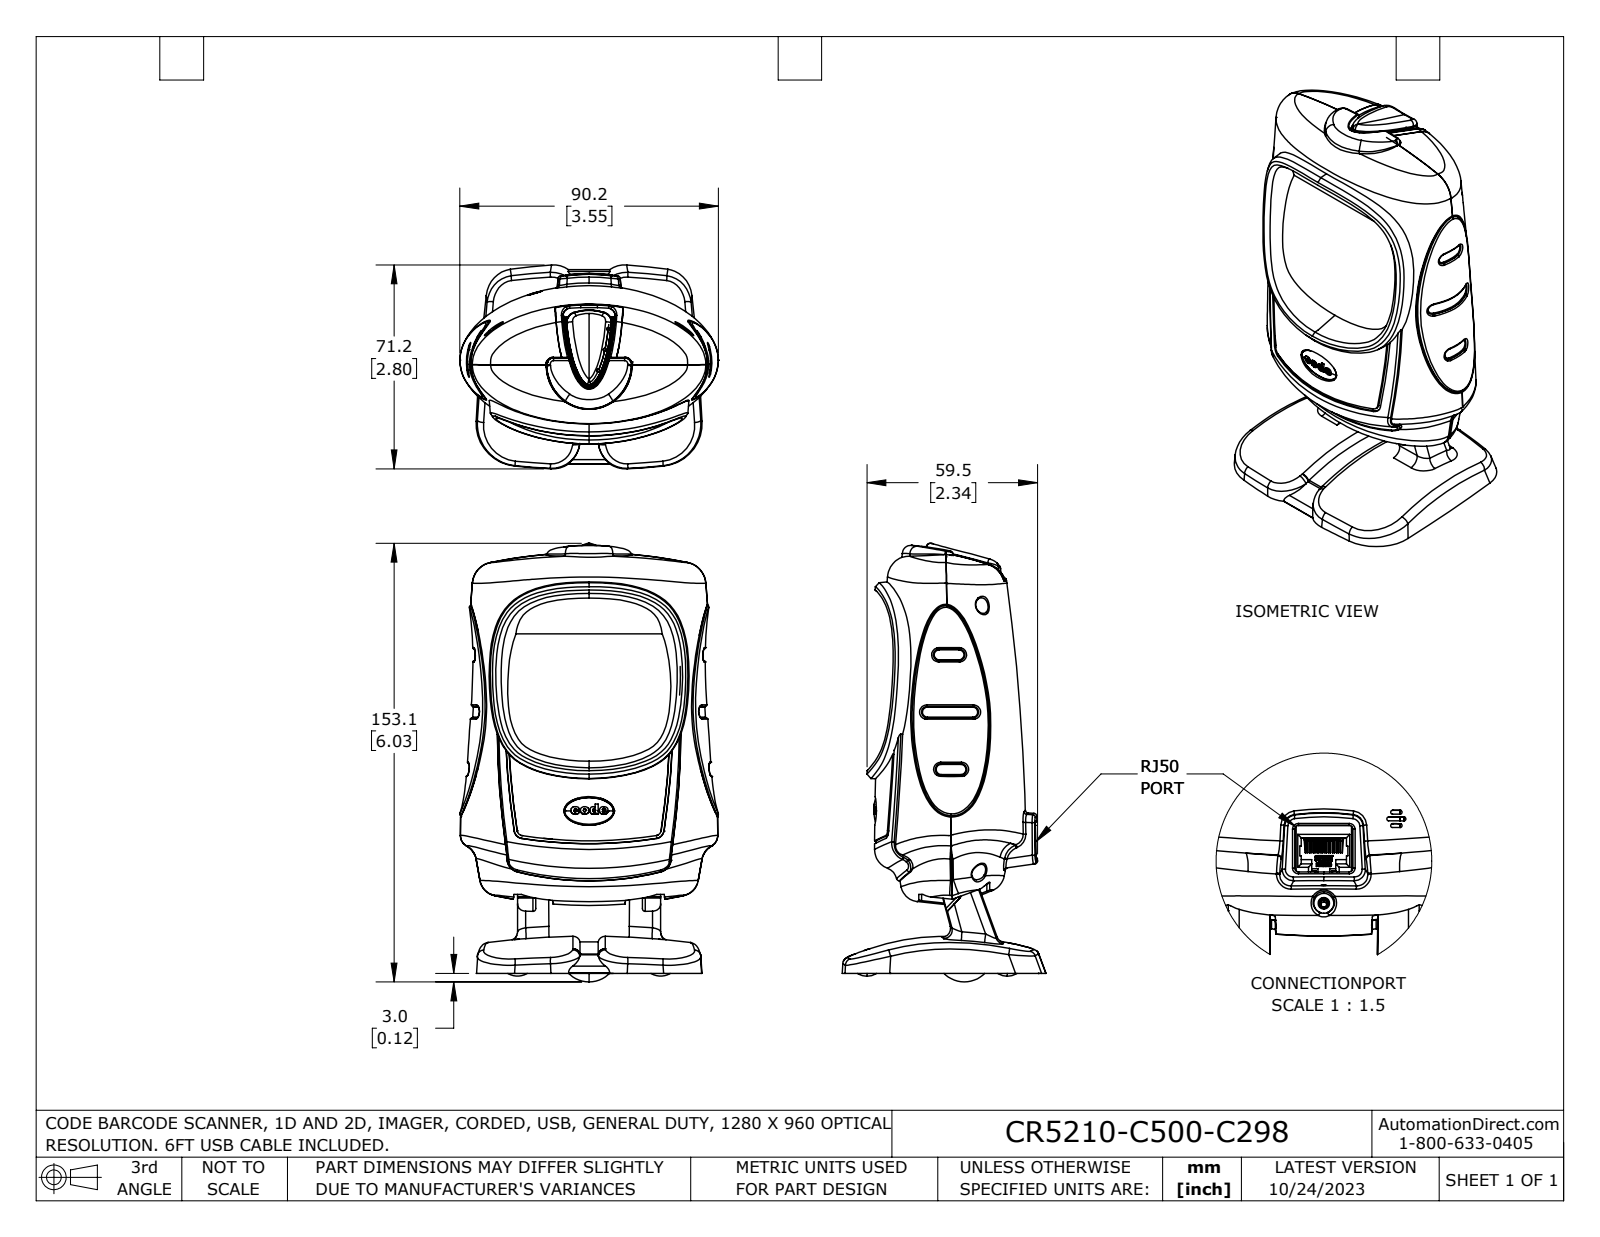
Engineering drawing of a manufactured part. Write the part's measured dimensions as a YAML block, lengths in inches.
part_name: "CR5210-C500-C298"
step_written_by: "SolidWorks 2023 (AUTOMOTIVE_DESIGN)"
units: inches
bodies: {solids: 1, faces: 1568, planar: 534, cylindrical: 166, other: 868}
overall_size: [6.03, 3.555, 2.804]
volume: 23.32
surface_area: 97.86
round_bosses_or_shafts:
  - {diameter: 0.344, count: 4}
  - {diameter: 0.167, count: 3}
  - {diameter: 0.079, count: 1}
partial_cylinders:
  - {radius: 0.039, count: 21}
  - {radius: 0.007, count: 18}
  - {radius: 0.013, count: 18}
  - {radius: 0.106, count: 16}
  - {radius: 0.02, count: 12}
  - {radius: 0.01, count: 8}
  - {radius: 0.059, count: 7}
  - {radius: 0.118, count: 4}
face_to_face_distances: [0.079, 0.059, 0.091, 1.969, 0.138, 0.118, 0.031, 0.047, 0.15, 0.197]
